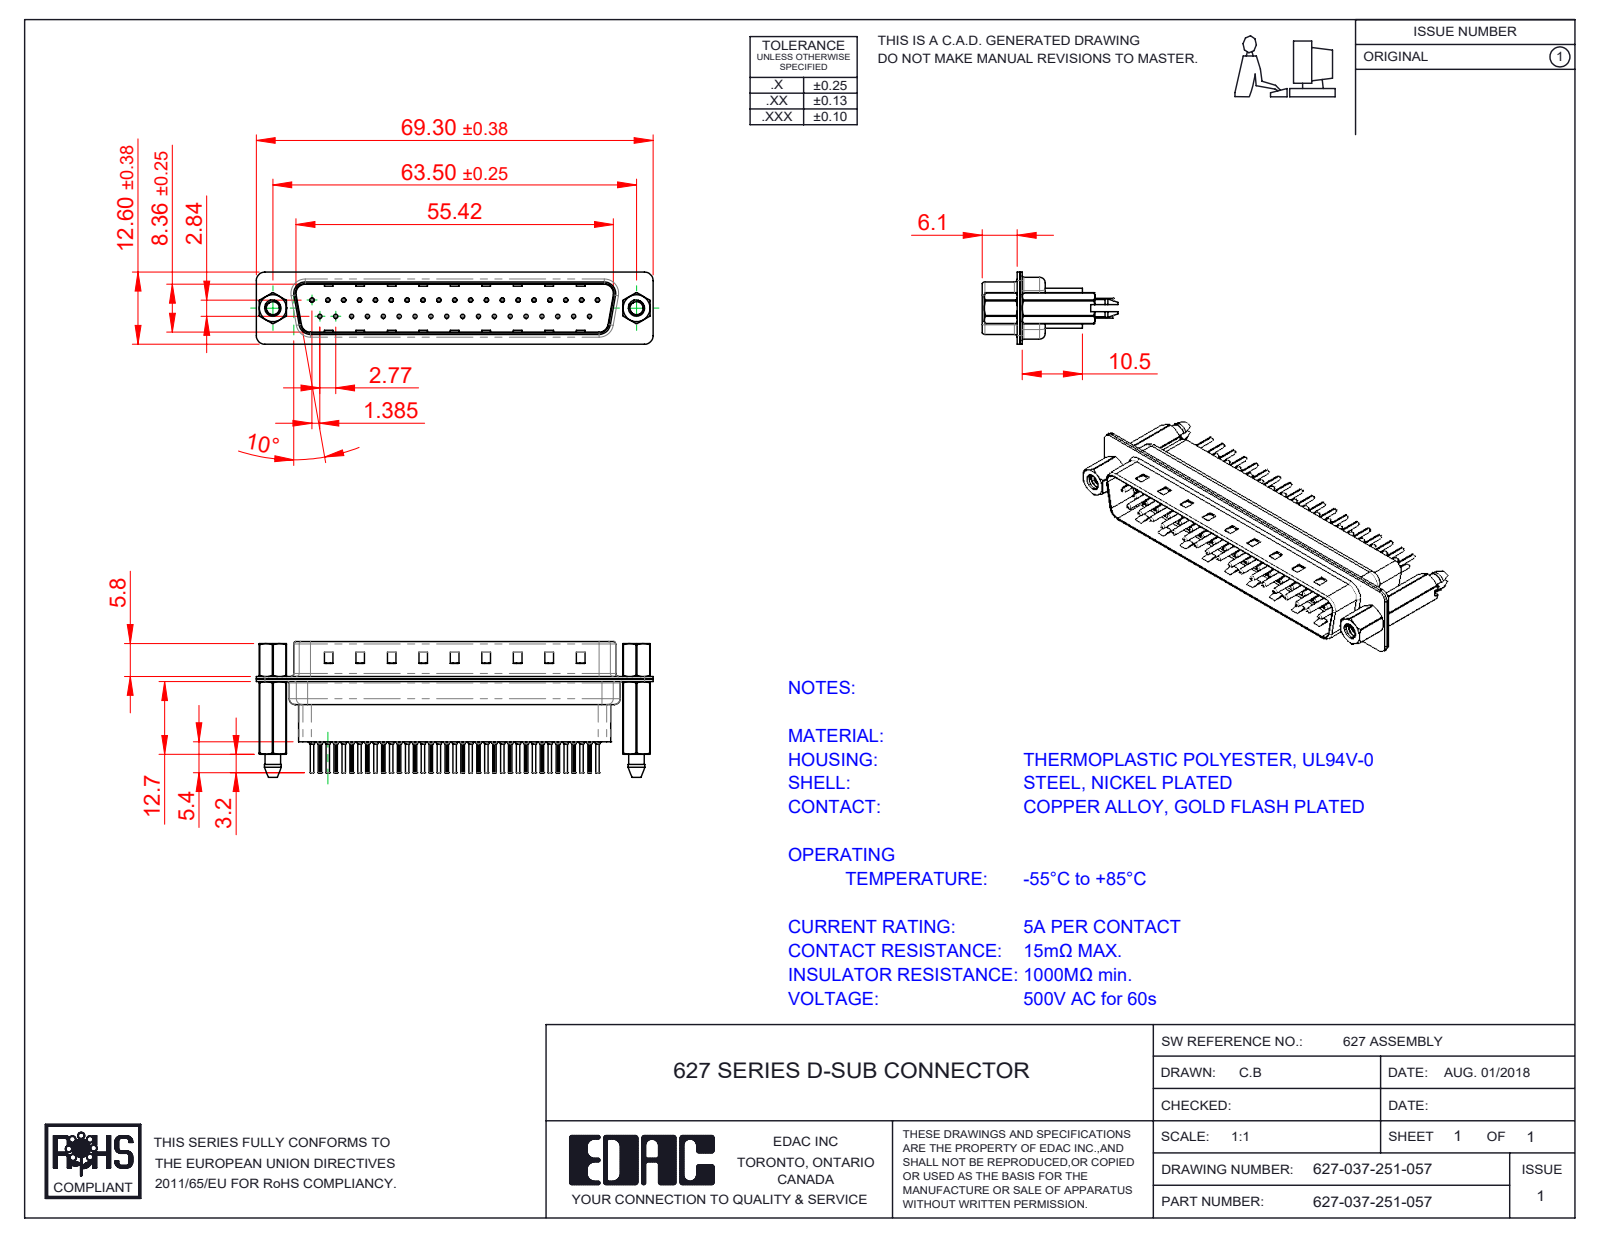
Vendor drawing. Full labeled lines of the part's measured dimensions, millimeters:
Part name (STEP PRODUCT): 627 Contact Row 2_41; 627-037-251-057; 627 Housing_37 HP; 627 4-40 Threaded Boardlock_HP51 (+4 more)
STEP written by: SolidWorks 2020 (CONFIG_CONTROL_DESIGN)
Units: millimetres
Bodies: 44 solids, 4272 faces (1145 planar, 1648 cylindrical, 1479 other)
Overall size (bounding box): 69.3 × 23.6 × 12.6
Volume: 5 848 mm³ · Surface area: 14 927 mm²
Round holes (diameter × count): ⌀0.2 ×37, ⌀0.35 ×37, ⌀1.1 ×37, ⌀1.6 ×37, ⌀2.26 ×2, ⌀2.29 ×2, ⌀4 ×2, ⌀4.8 ×2
Round bosses / shafts (diameter × count): ⌀2 ×37, ⌀1.5 ×37, ⌀0.75 ×37, ⌀0.6 ×37, ⌀4.9 ×2, ⌀2.79 ×2
Partial cylindrical surfaces — rounded edges, fillets, slot ends (radius × count): R0.1 ×74, R1.5 ×18, R2 ×12, R1.6 ×10, R0.5 ×8, R0.25 ×4, R0.6 ×4, R0.65 ×4
Main face-to-face distances: 0.4, 0.82, 9.58, 0.45, 0.68, 7.68, 1.5, 1.08, 8.08, 8.76
Hole centre spacings: 3.16, 2.77, 5.54, 8.31, 5.04, 10.1, 11.08, 12.78
